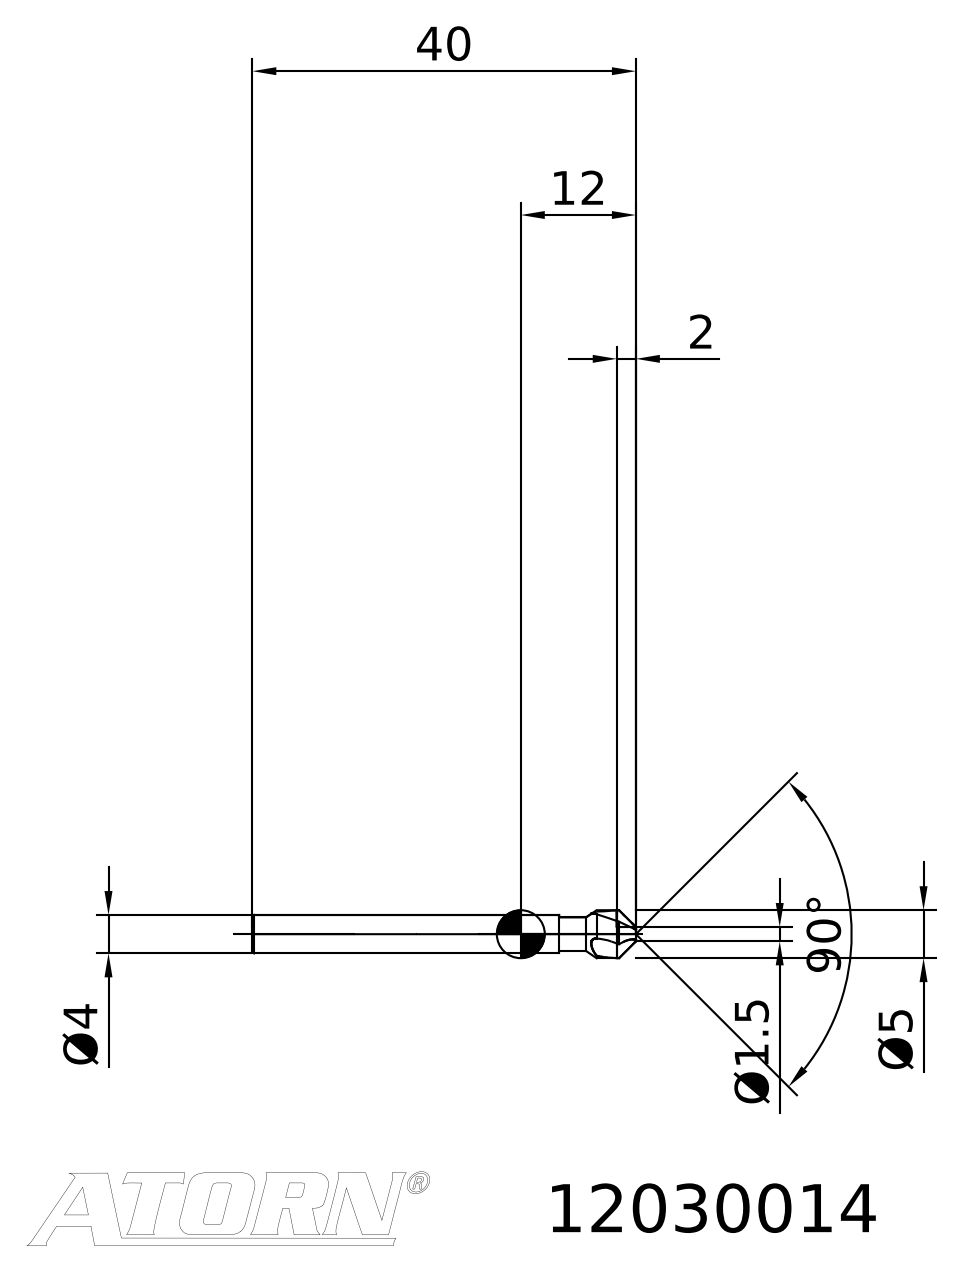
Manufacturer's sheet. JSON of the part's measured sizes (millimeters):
{"step_written_by": "TDM (AUTOMOTIVE_DESIGN)", "units": "millimeters", "bodies": {"solids": 2, "faces": 37, "planar": 17, "cylindrical": 0, "other": 20}, "overall_size": [40, 5, 5], "volume_mm3": 489, "surface_area_mm2": 556, "face_to_face_distances": [38, 6, 32, 2, 8, 40]}
